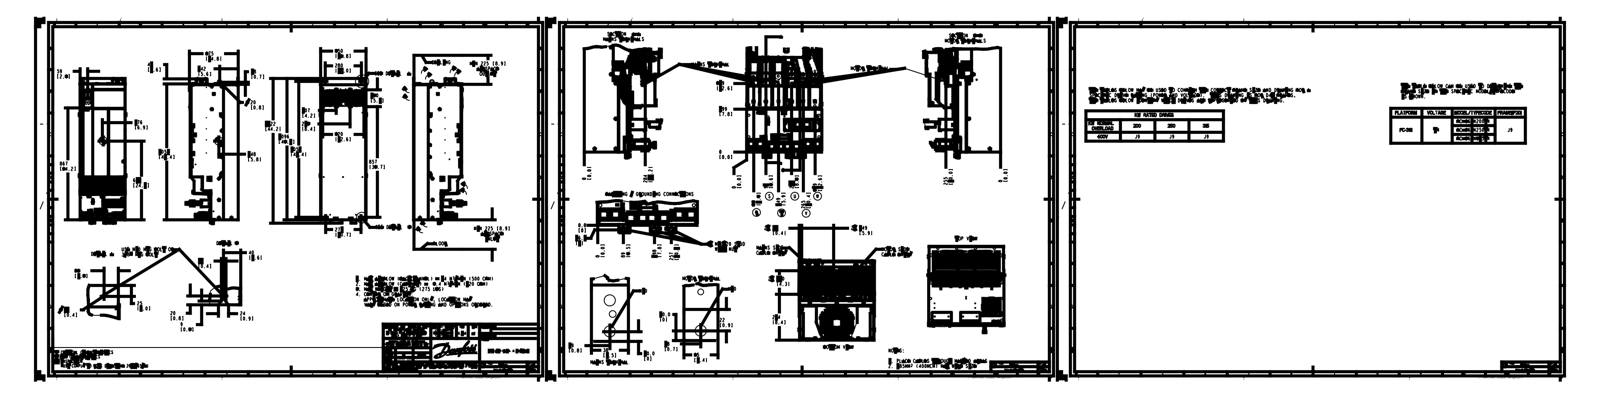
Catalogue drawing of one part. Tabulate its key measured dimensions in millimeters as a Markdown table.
| quantity | value |
| --- | --- |
| part name | P6036_J9_TOP_ASSEMBLY_MARKET_20 |
| STEP written by | CREO PARAMETRIC BY PTC INC, 2022124 (CONFIG_CONTROL_DESIGN) |
| units | millimeters |
| bodies | 90 solids, 16175 faces (9194 planar, 4615 cylindrical, 2366 other) |
| overall size | 1122.68 × 375.6 × 350 |
| volume | 1 797 000 mm³ |
| surface area | 4 234 000 mm² |
| round holes (diameter × count) | 8 × 32, 5 × 18, 4.2 × 12, 4 × 11, 4.5 × 11, 11 × 11, 6.5 × 9, 6.35 × 8, 5.5 × 6, 7.2 × 6, 16 × 6, 6 × 4 |
| round bosses / shafts (diameter × count) | 5 × 28, 4.2 × 26, 8.7 × 17, 8 × 14, 6.5 × 13, 10.8 × 12, 9.8 × 12, 6.4 × 12 |
| partial cylindrical surfaces (radius × count) | 1.5 × 616, 0.3 × 386, 3.2 × 376, 0.5 × 278, 4 × 184, 0.2 × 182, 1 × 182, 0.1 × 80 |
| main face-to-face distances | 1.9, 346.2, 348.1, 3.8, 344.3, 211.6, 350, 368.5, 366.6, 3.6 |
| hole center spacings | 130, 168.16, 15.1, 106.67, 213.33, 249.82, 402.74, 161.34 |
